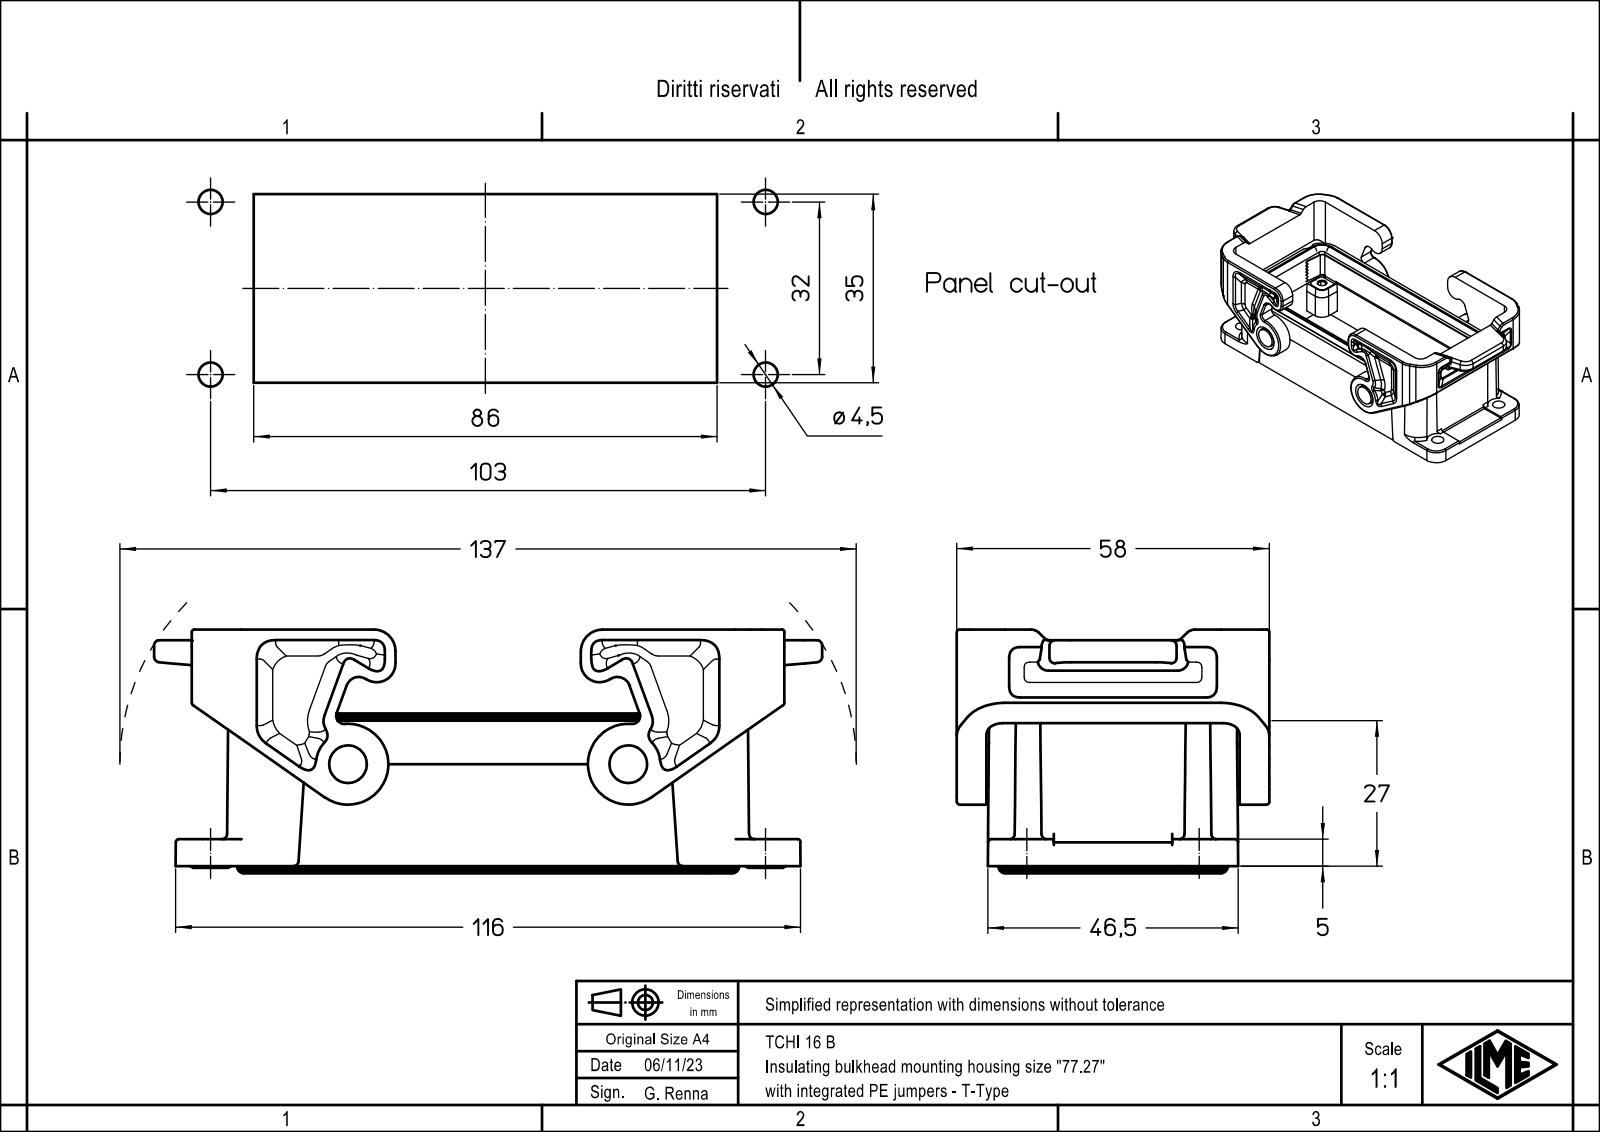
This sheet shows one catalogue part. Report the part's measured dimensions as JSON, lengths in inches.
{"part_name": "TCHI 16 B", "step_written_by": "Creo Elements/Direct Modeling 20.1B 02-Apr-2019 (C) Parametric Technology GmbH (AUTOMOTIVE_DESIGN)", "units": "inches", "bodies": {"solids": 1, "faces": 911, "planar": 464, "cylindrical": 261, "other": 186}, "overall_size": [4.882, 2.283, 1.781], "volume_in3": 4.305, "surface_area_in2": 64.19, "round_holes": [[0.098, 4], [0.138, 4], [0.177, 4], [0.283, 2]], "round_bosses_or_shafts": [[0.189, 4], [0.276, 2]], "partial_cylinders_radius": [[0.039, 29], [0.051, 20], [0.059, 18], [0.079, 16], [0.106, 12], [0.118, 12], [0.217, 12], [0.197, 8]], "face_to_face_distances": [0.232, 1.618, 1.386, 1.591, 0.217, 1.807, 0.449, 1.835, 2.067, 0.26], "hole_center_spacings": [0.511, 1.265, 3.554, 3.738, 1.063, 1.26, 3.051, 3.231]}
